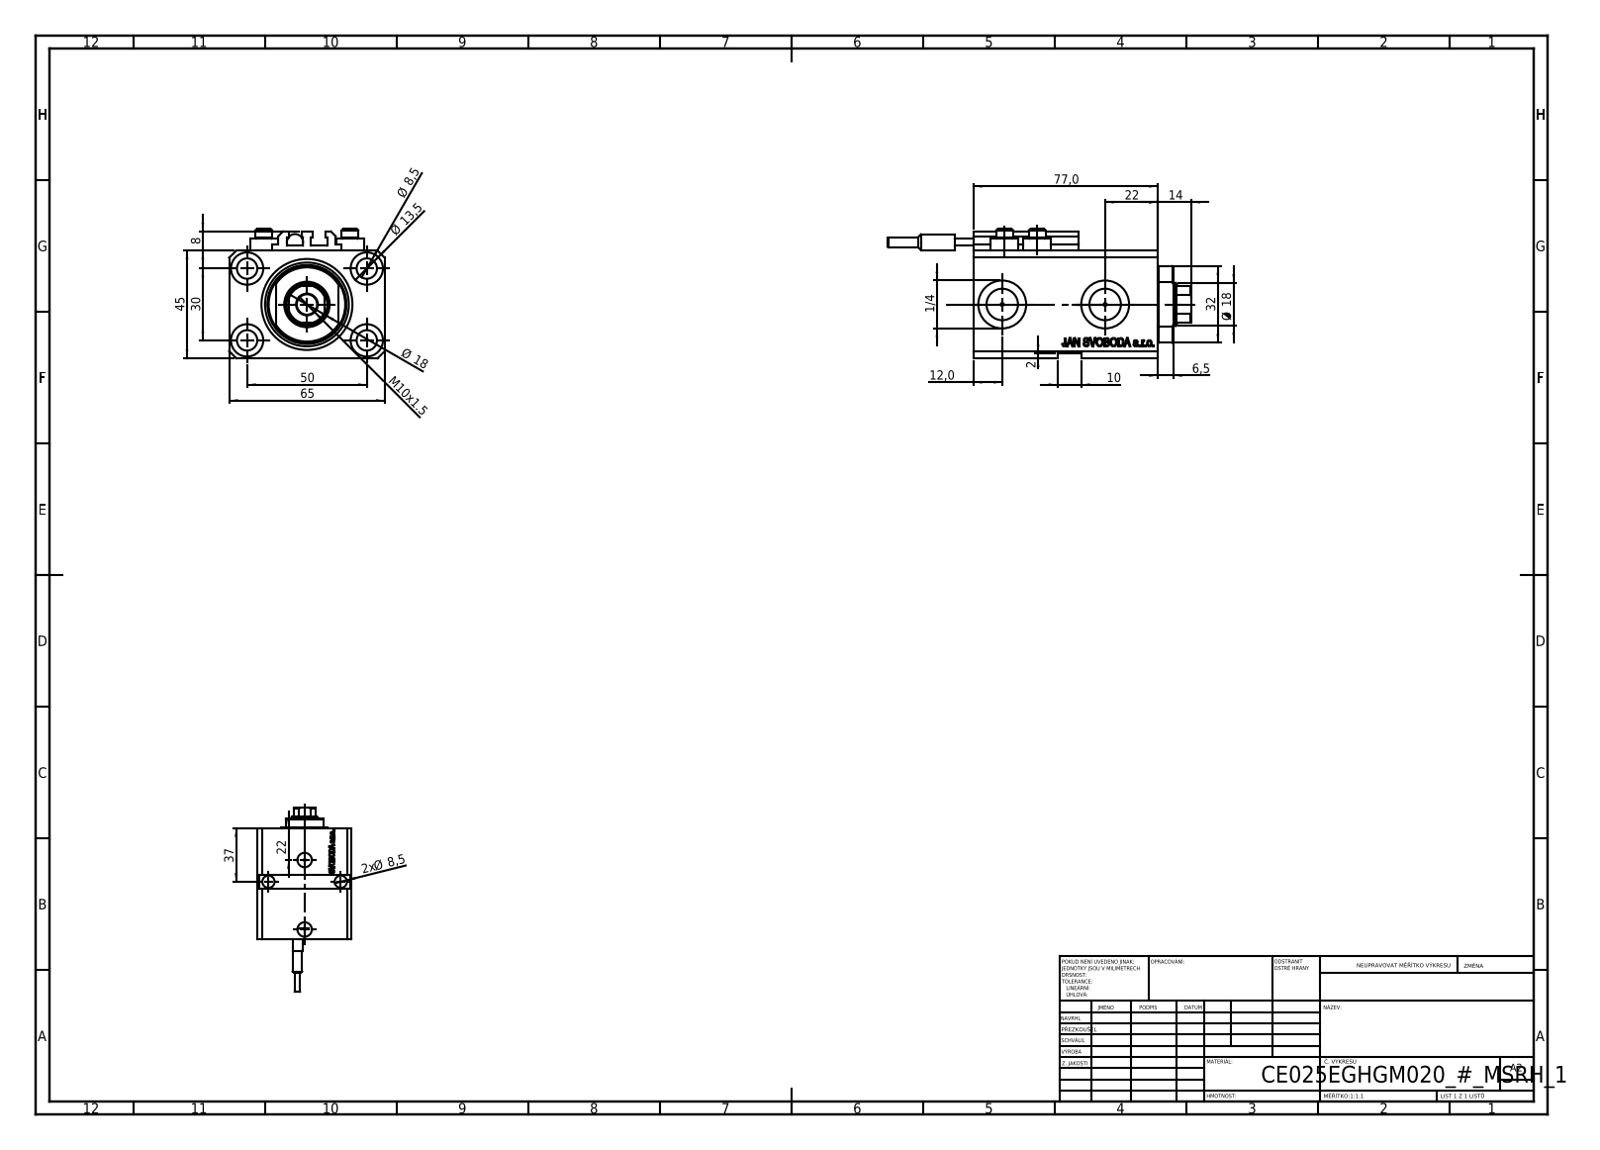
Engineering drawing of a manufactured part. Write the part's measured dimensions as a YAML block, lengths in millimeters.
part_name: "V250CE_E_Body; SWITCH_V250CE; V250CE_C_VCP; V250CE_VC_E (+1 more)"
step_written_by: "SolidWorks 2019 (CONFIG_CONTROL_DESIGN)"
units: millimeters
bodies: {solids: 9, faces: 1093, planar: 527, cylindrical: 132, other: 434}
overall_size: [127, 65, 54]
volume: 201561
surface_area: 60560
round_holes:
  - {diameter: 8.5, count: 7}
  - {diameter: 1.25, count: 4}
  - {diameter: 4, count: 4}
  - {diameter: 13.5, count: 4}
  - {diameter: 10, count: 2}
  - {diameter: 13.16, count: 2}
  - {diameter: 20, count: 2}
  - {diameter: 18, count: 1}
  - {diameter: 25, count: 1}
  - {diameter: 38, count: 1}
round_bosses_or_shafts:
  - {diameter: 11.6, count: 4}
  - {diameter: 7, count: 4}
  - {diameter: 6.8, count: 1}
  - {diameter: 6.5, count: 1}
  - {diameter: 4, count: 1}
partial_cylinders:
  - {radius: 0.2, count: 10}
  - {radius: 8.5, count: 1}
  - {radius: 16, count: 1}
face_to_face_distances: [45, 65, 63, 14, 2, 77, 3, 47, 5, 6.9]
hole_center_spacings: [29.15, 50, 13.6, 15.12, 18.81, 18.97, 26.22, 26.61]
